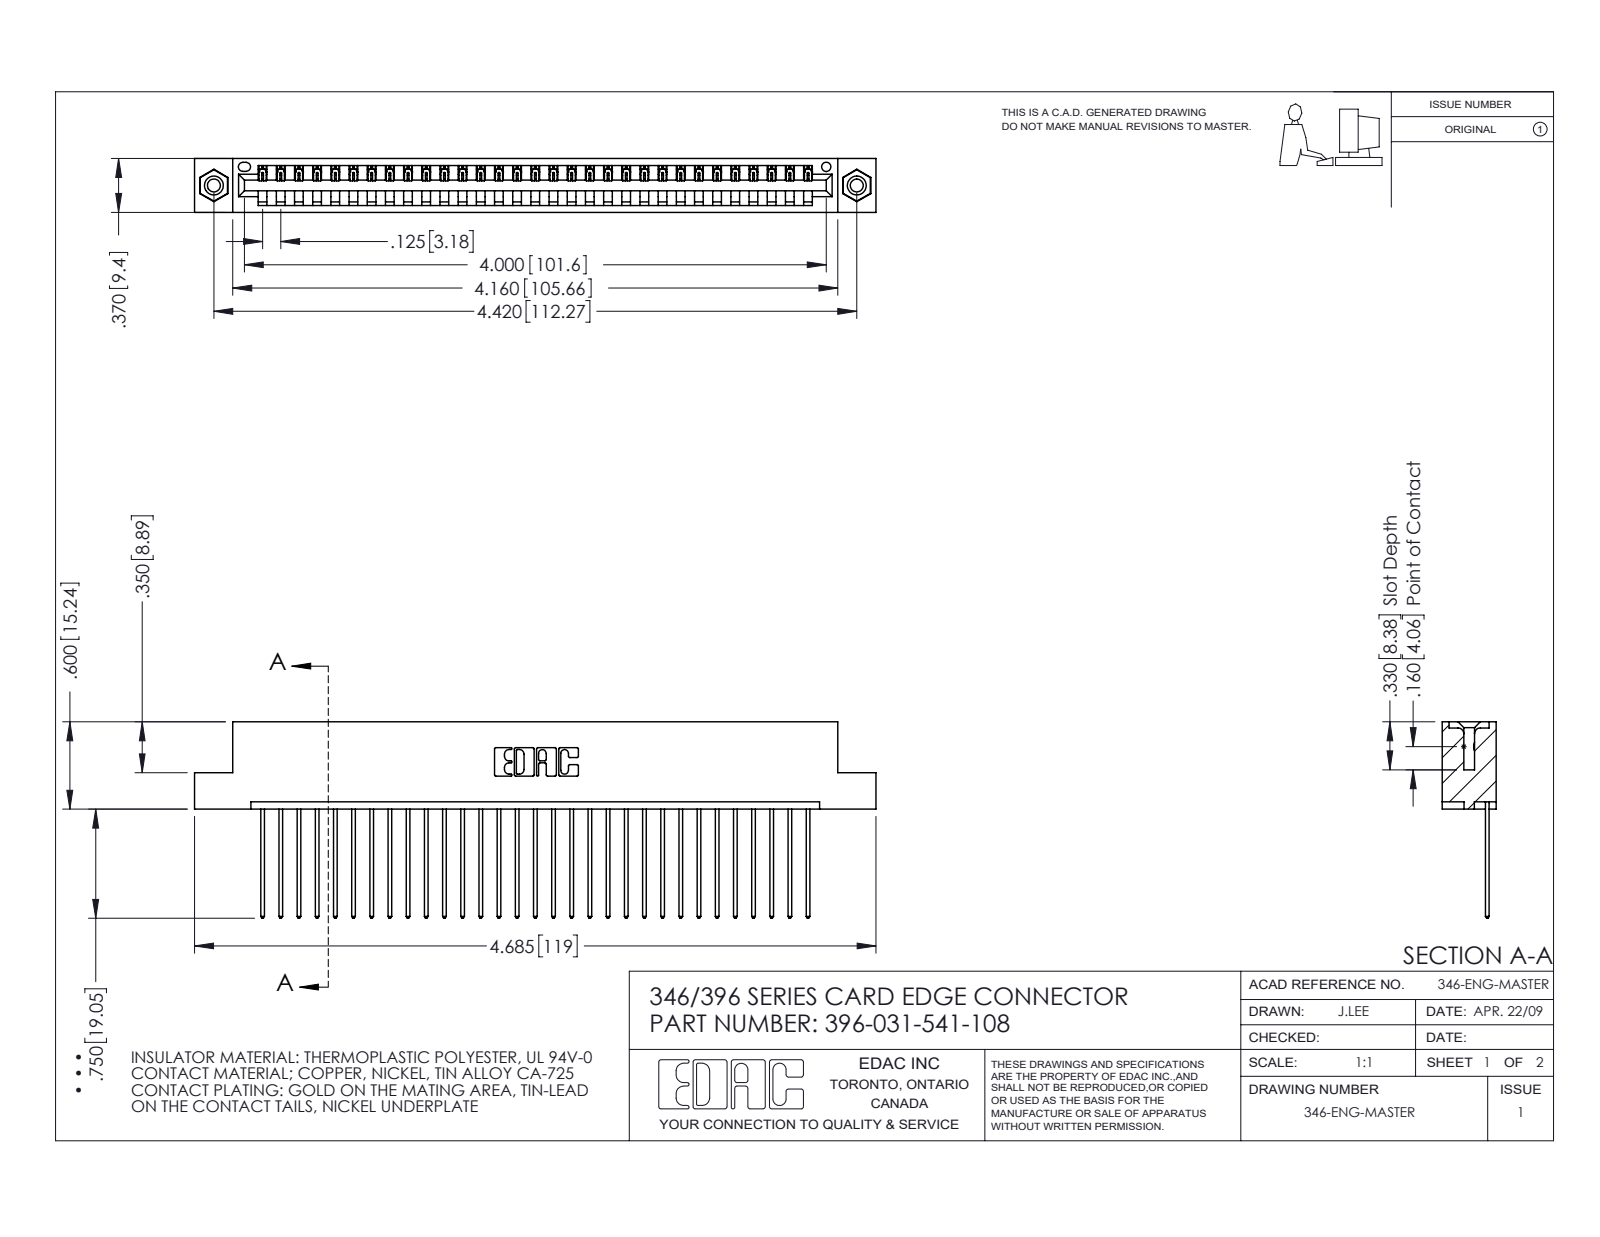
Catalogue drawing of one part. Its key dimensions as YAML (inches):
part_name: "345-250-001_345-250-003-102; 346 Part_Flush Mounting Lugs - 0.156 Dia-TI; 345-292-001_345-293-141; 396-031-541-108"
step_written_by: "SolidWorks 2016 (CONFIG_CONTROL_DESIGN)"
units: inches
bodies: {solids: 34, faces: 1980, planar: 1348, cylindrical: 616, other: 16}
overall_size: [4.685, 1.35, 0.37]
volume: 0.696
surface_area: 22.9
round_holes:
  - {diameter: 0.089, count: 2}
  - {diameter: 0.125, count: 2}
  - {diameter: 0.156, count: 2}
  - {diameter: 0.064, count: 1}
round_bosses_or_shafts:
  - {diameter: 0.155, count: 2}
partial_cylinders:
  - {radius: 0.006, count: 62}
  - {radius: 0.01, count: 62}
  - {radius: 0.01, count: 22}
  - {radius: 0.007, count: 6}
  - {radius: 0.031, count: 6}
  - {radius: 0.026, count: 3}
  - {radius: 0.031, count: 2}
  - {radius: 0.04, count: 2}
face_to_face_distances: [0.048, 0.322, 0.37, 0.25, 0.072, 0.298, 0.025, 0.148, 0.222, 0.1]
hole_center_spacings: [0.246, 4.212, 4.42]
